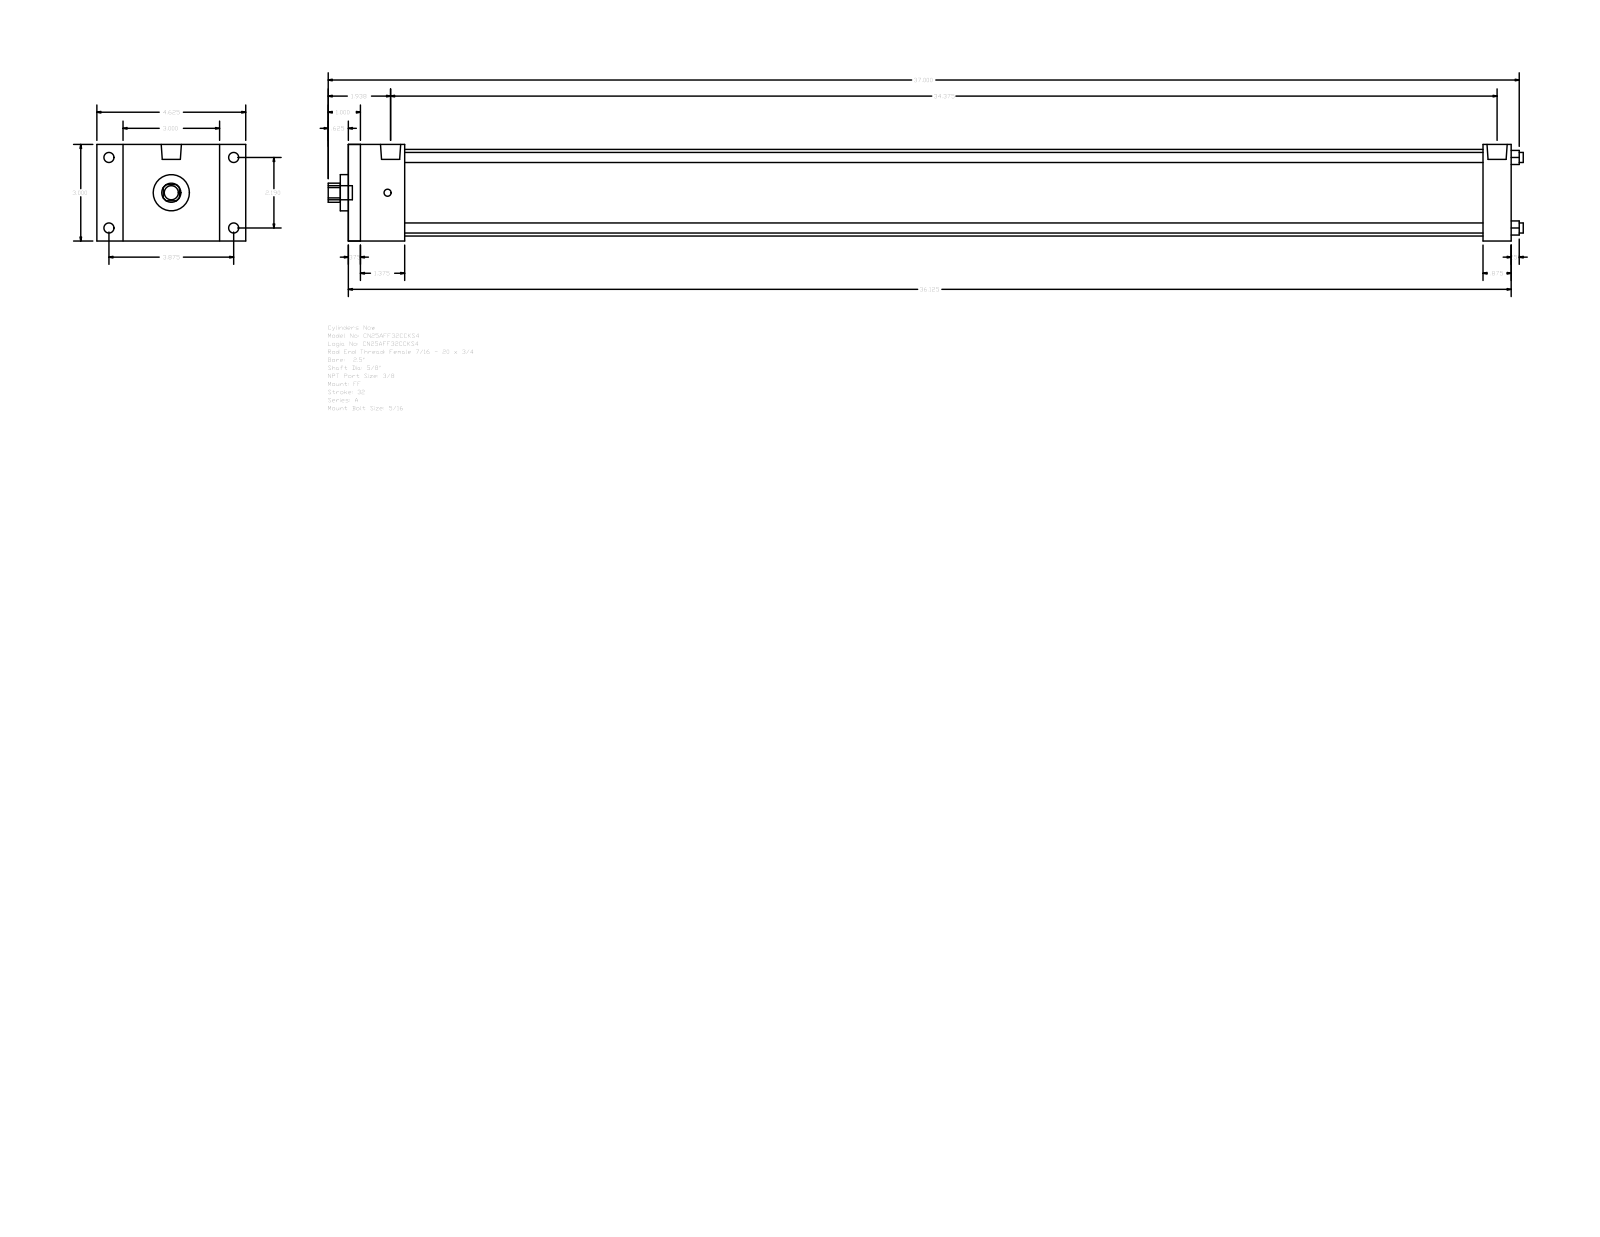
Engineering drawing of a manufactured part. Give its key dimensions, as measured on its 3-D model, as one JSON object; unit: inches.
{"part_name": "A_FF__0250_0.625", "step_written_by": "GSSL Pune (CONFIG_CONTROL_DESIGN)", "units": "inches", "bodies": {"solids": 0, "faces": 92, "planar": 64, "cylindrical": 28, "other": 0}, "overall_size": [37.125, 4.625, 3], "round_holes": [[0.313, 4], [0.625, 1], [1.125, 1], [2.69, 1]], "round_bosses_or_shafts": [[0.313, 4], [0.219, 4], [0.627, 2], [0.437, 1]], "partial_cylinders_radius": [[0.297, 1]], "face_to_face_distances": [3, 36.125, 0.375, 35.75, 1.75, 35.25, 1.375, 34.875, 33.5, 34.375], "hole_center_spacings": [1.548, 2.19, 3.097]}
